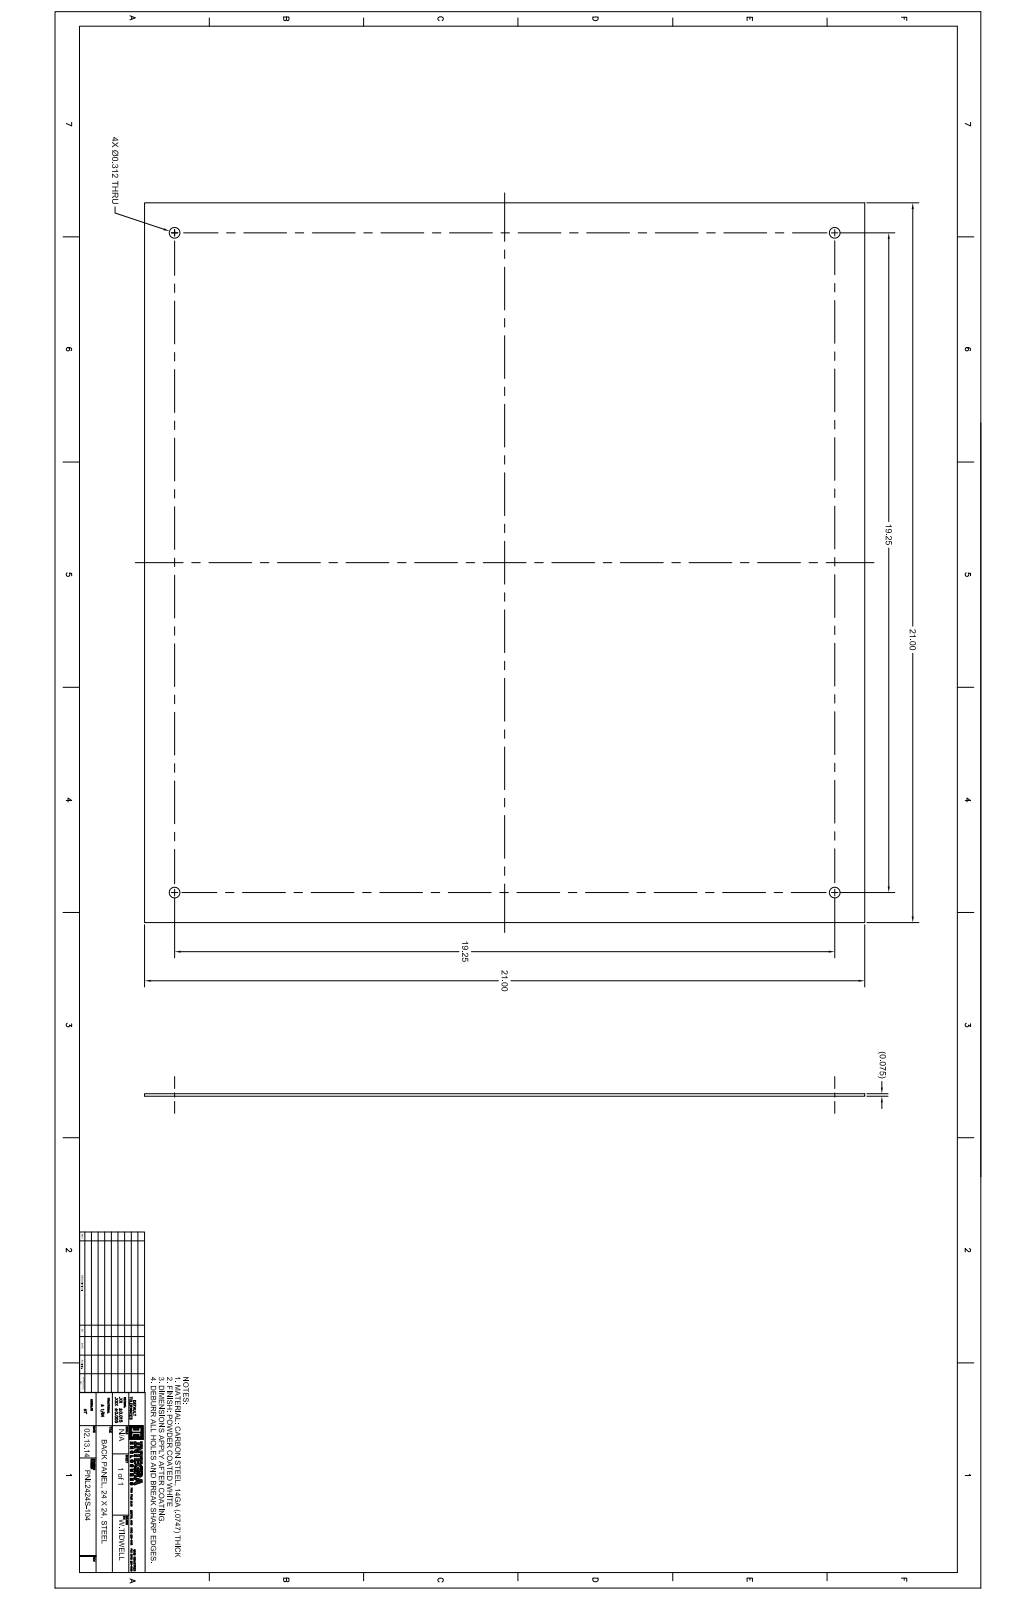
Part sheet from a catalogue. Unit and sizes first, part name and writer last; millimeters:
Units: millimetres
Overall size (bounding box): 533.4 × 533.4 × 1.9
Round holes (diameter × count): ⌀7.9 ×4
Main face-to-face distances: 1.9, 533.4
Hole centre spacings: 489, 691.5
Volume: 539 500 mm³ · Surface area: 572 900 mm²
Bodies: 1 solid, 10 faces (6 planar, 4 cylindrical, 0 other)
Part name (STEP PRODUCT): SBP-2424-P10
STEP written by: SolidWorks 2018 (AUTOMOTIVE_DESIGN)
